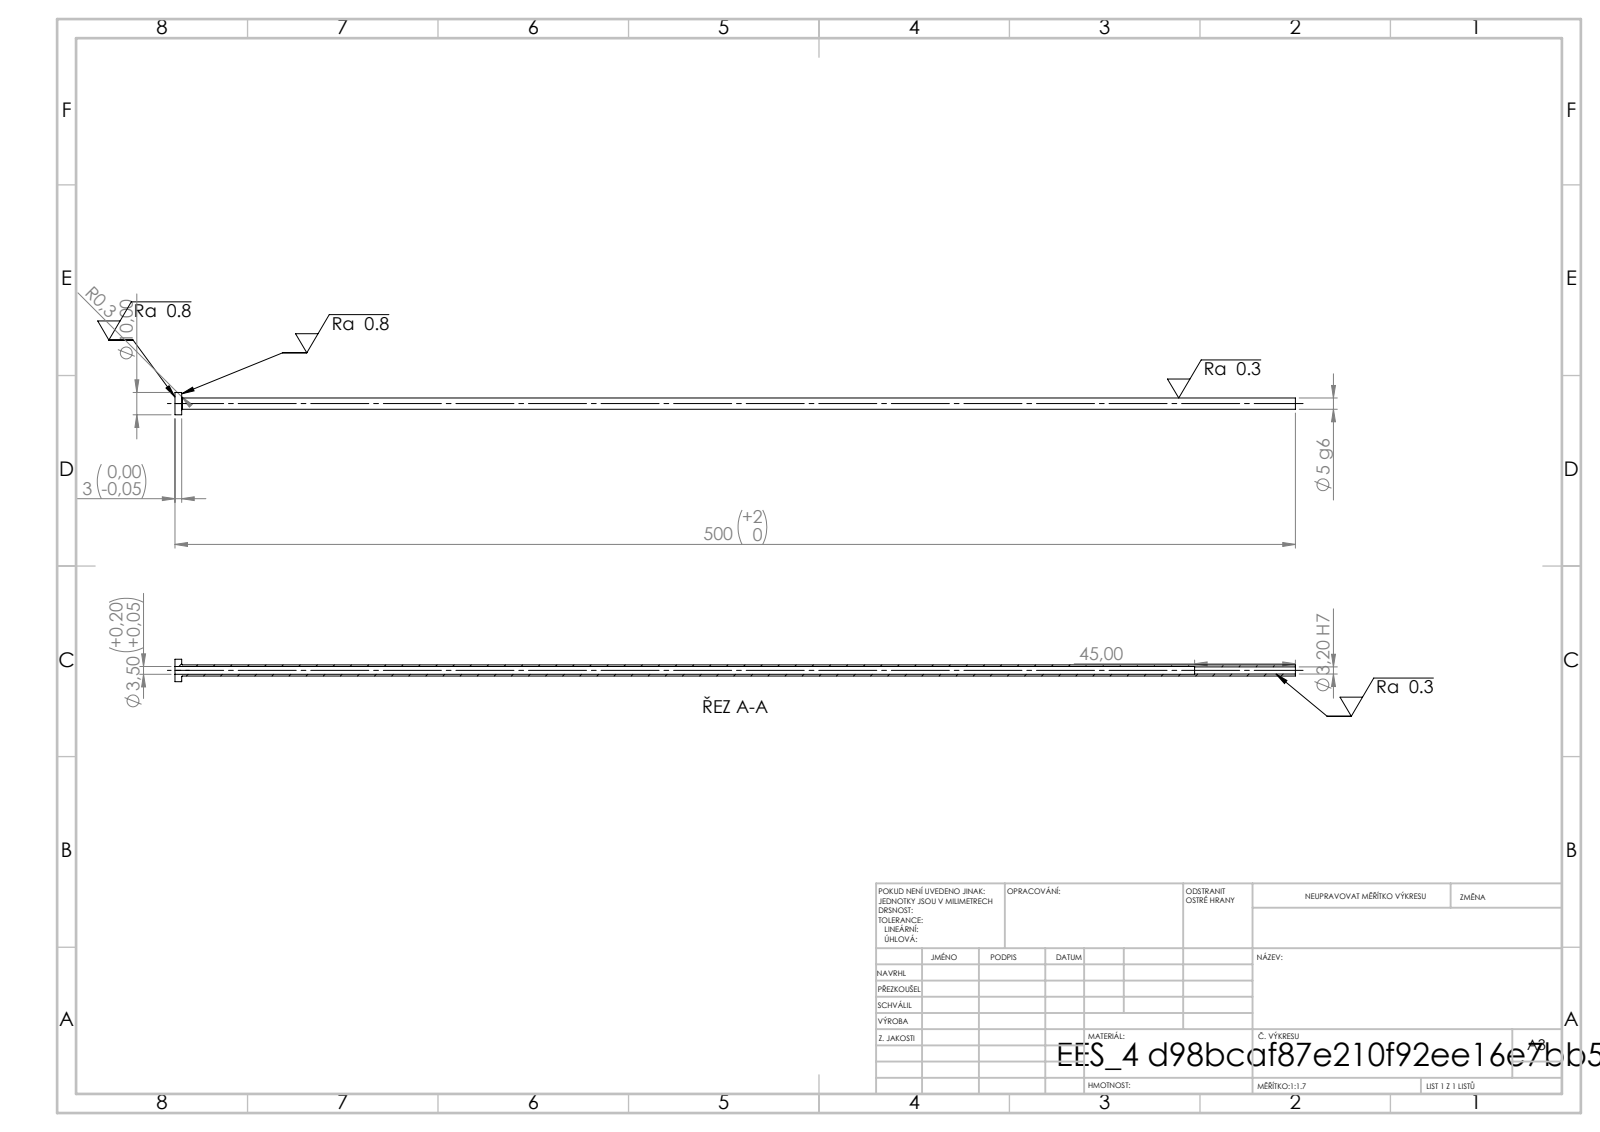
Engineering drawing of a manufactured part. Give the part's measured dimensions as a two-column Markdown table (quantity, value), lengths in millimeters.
| quantity | value |
| --- | --- |
| STEP written by | SolidWorks 2019 (CONFIG_CONTROL_DESIGN) |
| units | millimeters |
| bodies | 1 solid, 14 faces (4 planar, 8 cylindrical, 2 other) |
| overall size | 500 × 10 × 10 |
| volume | 5 255 mm³ |
| surface area | 13 495 mm² |
| round holes (diameter × count) | 3.2 × 1, 3.5 × 1 |
| round bosses / shafts (diameter × count) | 10 × 1, 5 × 1 |
| main face-to-face distances | 3, 500, 497, 455, 452, 45 |
